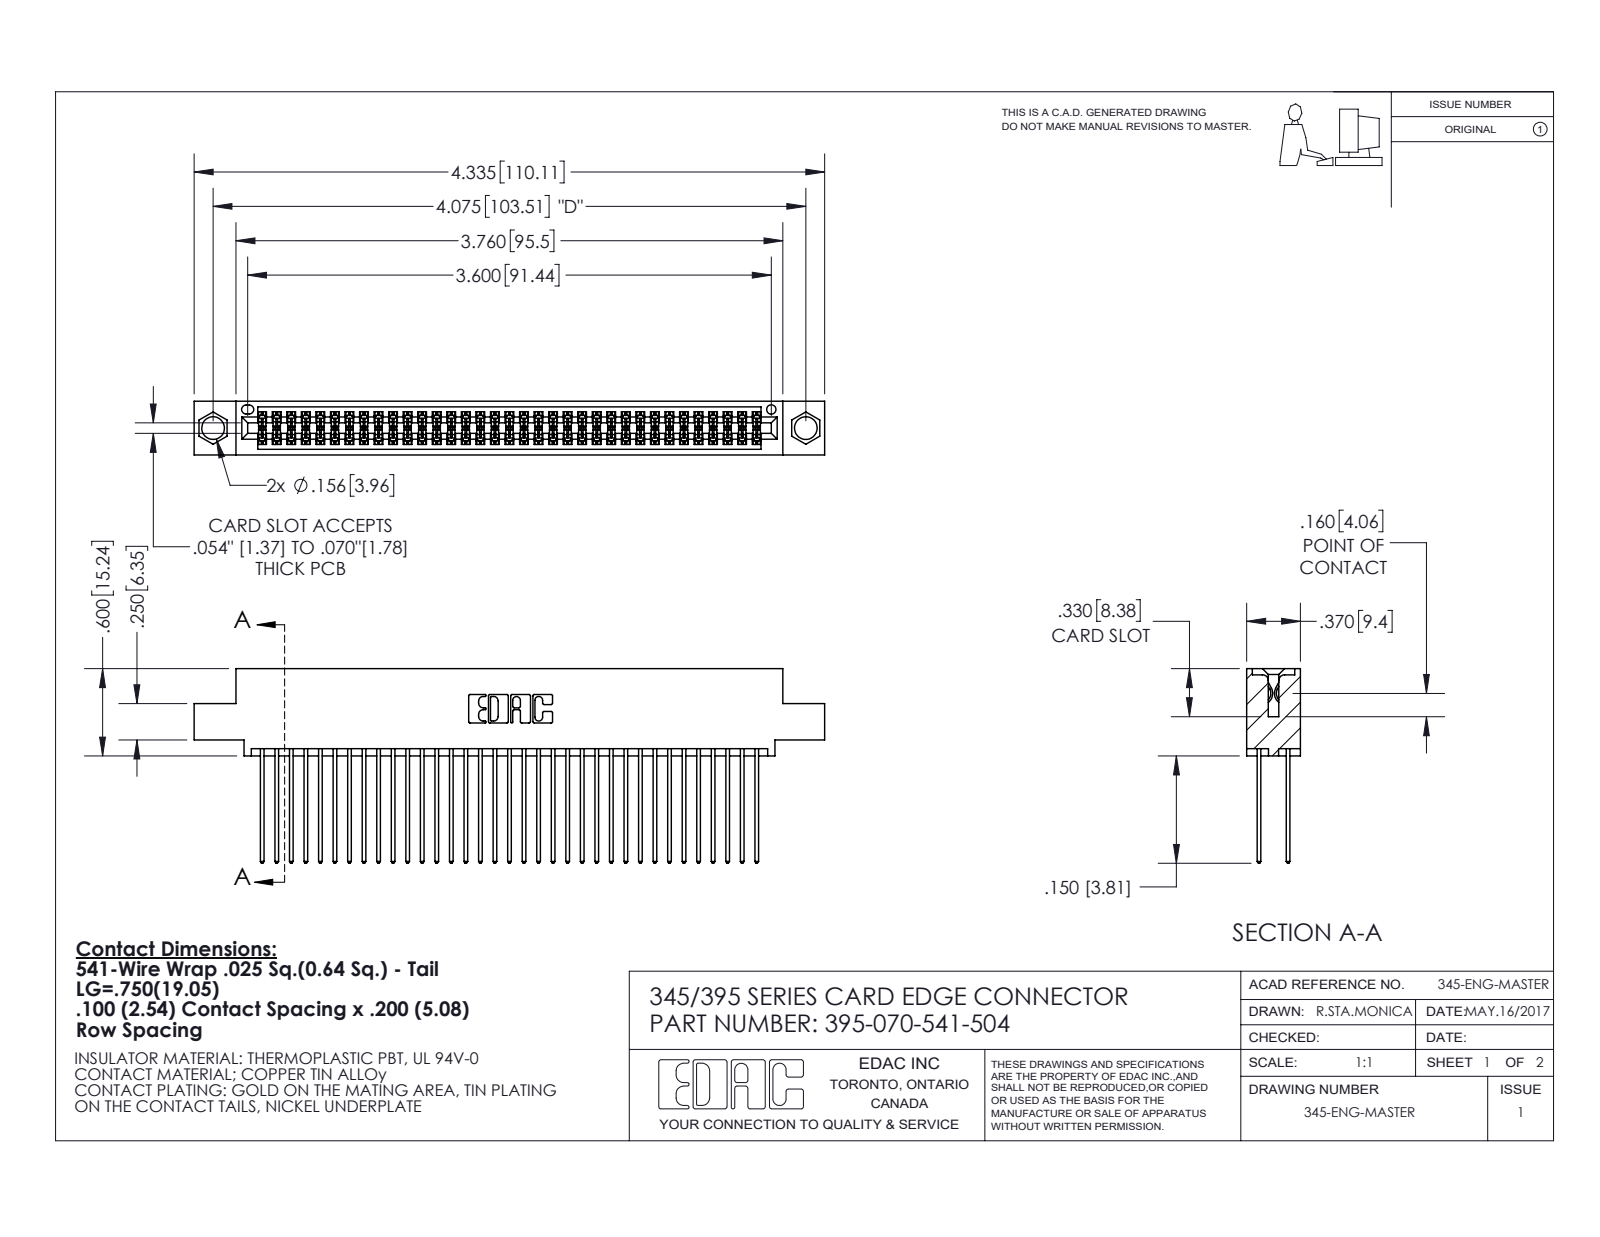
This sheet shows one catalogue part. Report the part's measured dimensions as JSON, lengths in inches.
{"part_name": "345-292-001_345-293-141; 395-070-541-504; 345 Part_0.110 Offset - 0.156 Dia-TI", "step_written_by": "SolidWorks 2020 (CONFIG_CONTROL_DESIGN)", "units": "inches", "bodies": {"solids": 71, "faces": 3644, "planar": 2408, "cylindrical": 1236, "other": 0}, "overall_size": [4.335, 1.337, 0.37], "volume_in3": 0.662, "surface_area_in2": 27.5, "round_holes": [[0.156, 2], [0.064, 1]], "partial_cylinders_radius": [[0.006, 140], [0.01, 70], [0.01, 22], [0.007, 6], [0.031, 6], [0.026, 3], [0.014, 2], [0.019, 2]], "face_to_face_distances": [0.072, 0.298, 0.2, 0.098, 0.272, 0.025, 0.225, 0.37, 0.175, 0.149], "hole_center_spacings": [0.27, 3.839, 4.075]}
